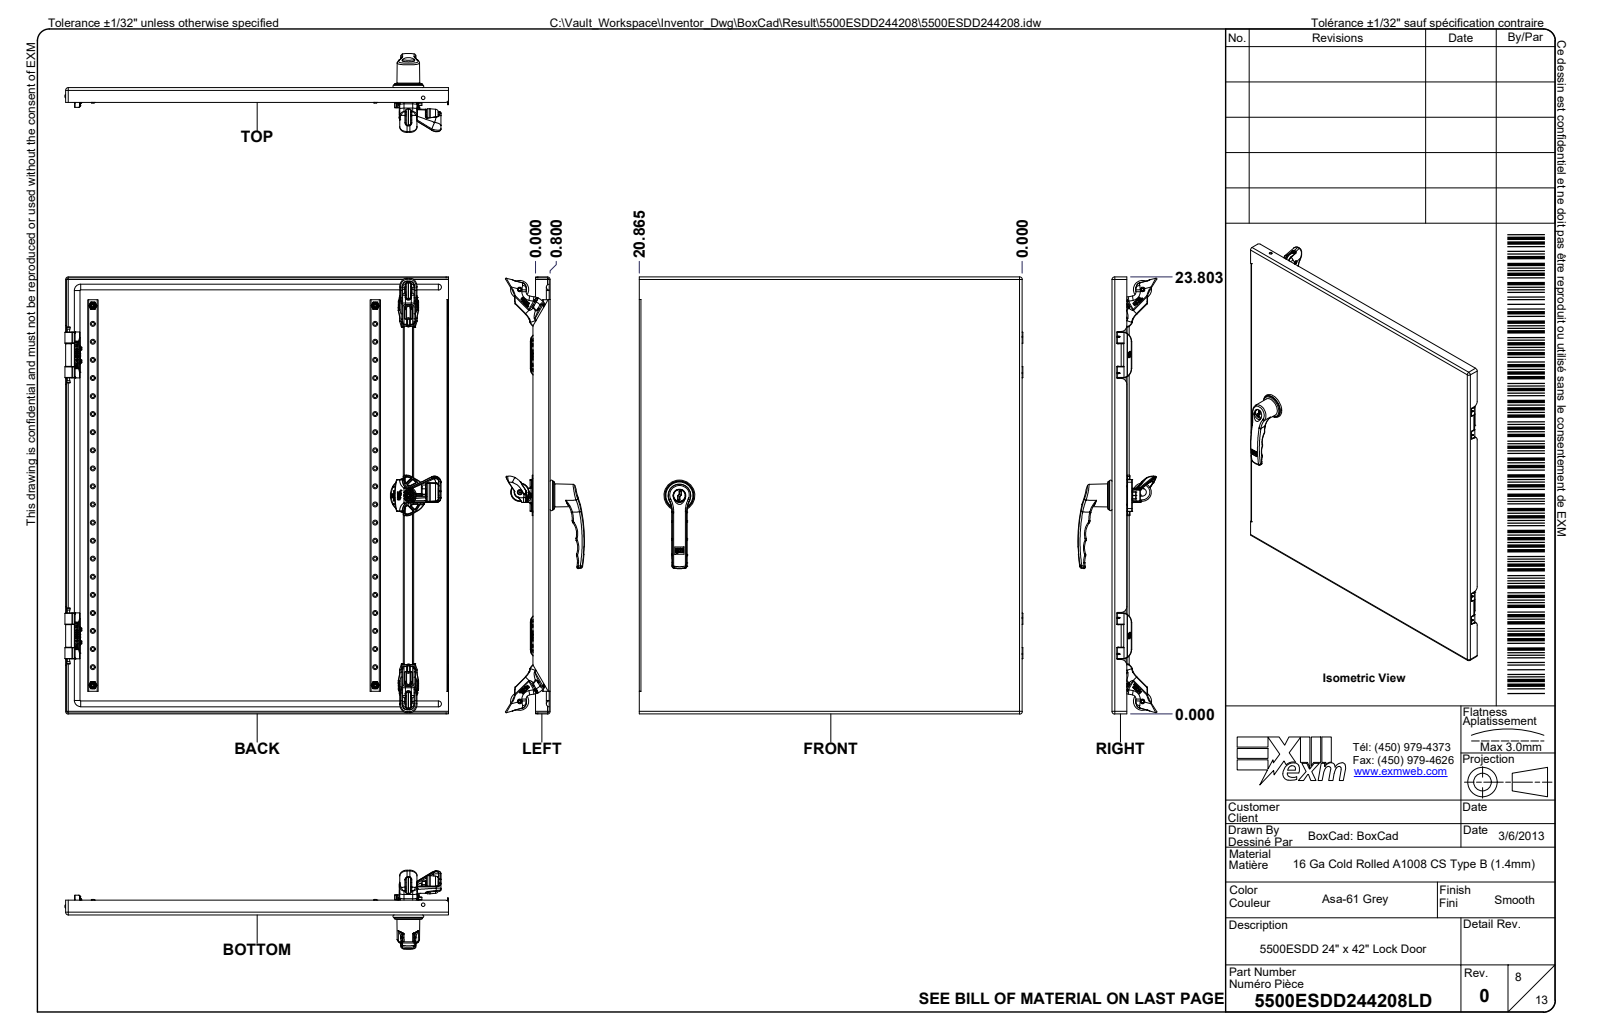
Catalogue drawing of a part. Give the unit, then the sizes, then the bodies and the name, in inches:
Units: inches
Overall size (bounding box): 42.006 × 24 × 10.97
Round holes (diameter × count): ⌀0.165 ×80, ⌀0.03 ×17, ⌀0.315 ×14, ⌀0.043 ×12, ⌀0.201 ×11, ⌀0.311 ×11, ⌀0.167 ×10, ⌀0.197 ×8, ⌀0.268 ×8, ⌀0.27 ×6, ⌀0.305 ×6, ⌀0.178 ×4
Round bosses / shafts (diameter × count): ⌀0.237 ×80, ⌀0.03 ×17, ⌀0.232 ×12, ⌀0.039 ×12, ⌀0.374 ×8, ⌀0.177 ×8, ⌀0.717 ×6, ⌀0.311 ×6
Partial cylindrical surfaces — rounded edges, fillets, slot ends (radius × count): R0.02 ×321, R0.039 ×258, R0.01 ×254, R0.008 ×124, R0.016 ×67, R0.079 ×67, R0.031 ×65, R0.004 ×36
Main face-to-face distances: 0.053, 0.053, 8.998, 9.052, 9.104, 9.051, 0.927, 0.874, 8.124, 8.177
Hole centre spacings: 1.969, 0.984, 15.303, 0.355, 0.394, 2.953, 3.937, 0.35
Volume: 313.1 in³ · Surface area: 9 521 in²
Bodies: 111 solids, 17730 faces (4359 planar, 4681 cylindrical, 8690 other)
Part name (STEP PRODUCT): 5500ESDD244208; 5500ESDD244208B; 5500ESDD244208B-P; STK-Q-16005 (+8 more)
STEP written by: Autodesk Inventor 2024 (AUTOMOTIVE_DESIGN)
